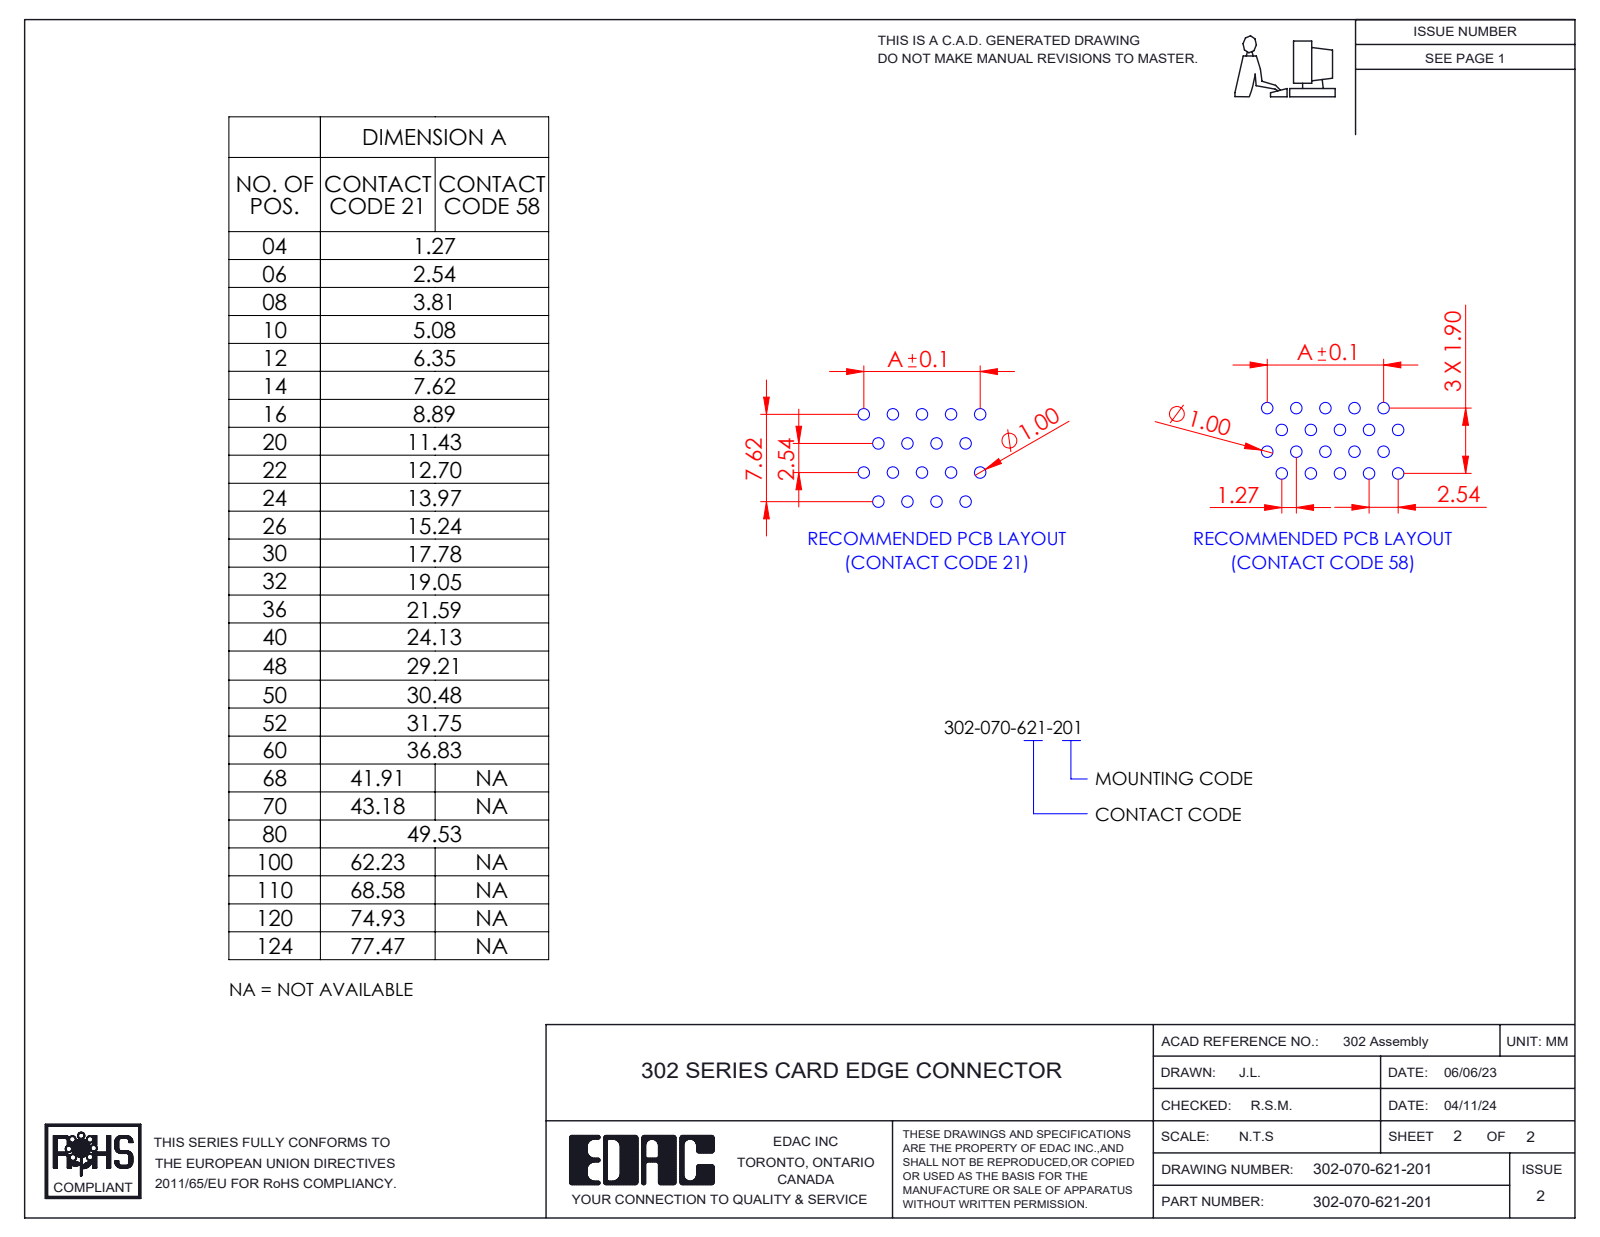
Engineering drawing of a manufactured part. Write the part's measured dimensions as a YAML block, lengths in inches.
part_name: "HSG_Vertical HSG; 302-070-621-201; Contact_302-290-X21 (2); Contact_302-290-X21 (1)"
step_written_by: "SolidWorks 2023 (CONFIG_CONTROL_DESIGN)"
units: inches
bodies: {solids: 71, faces: 3251, planar: 2394, cylindrical: 713, other: 144}
overall_size: [1.99, 0.694, 0.35]
volume: 0.24
surface_area: 16.66
partial_cylinders:
  - {radius: 0.008, count: 78}
  - {radius: 0.08, count: 4}
  - {radius: 0.082, count: 4}
  - {radius: 0.004, count: 2}
  - {radius: 0.016, count: 2}
  - {radius: 0.016, count: 2}
  - {radius: 0.049, count: 2}
  - {radius: 0.06, count: 2}
face_to_face_distances: [0.1, 0.05, 0.2, 0.15, 0.3, 0.25, 0.35, 0.35, 0.4, 0.45]
